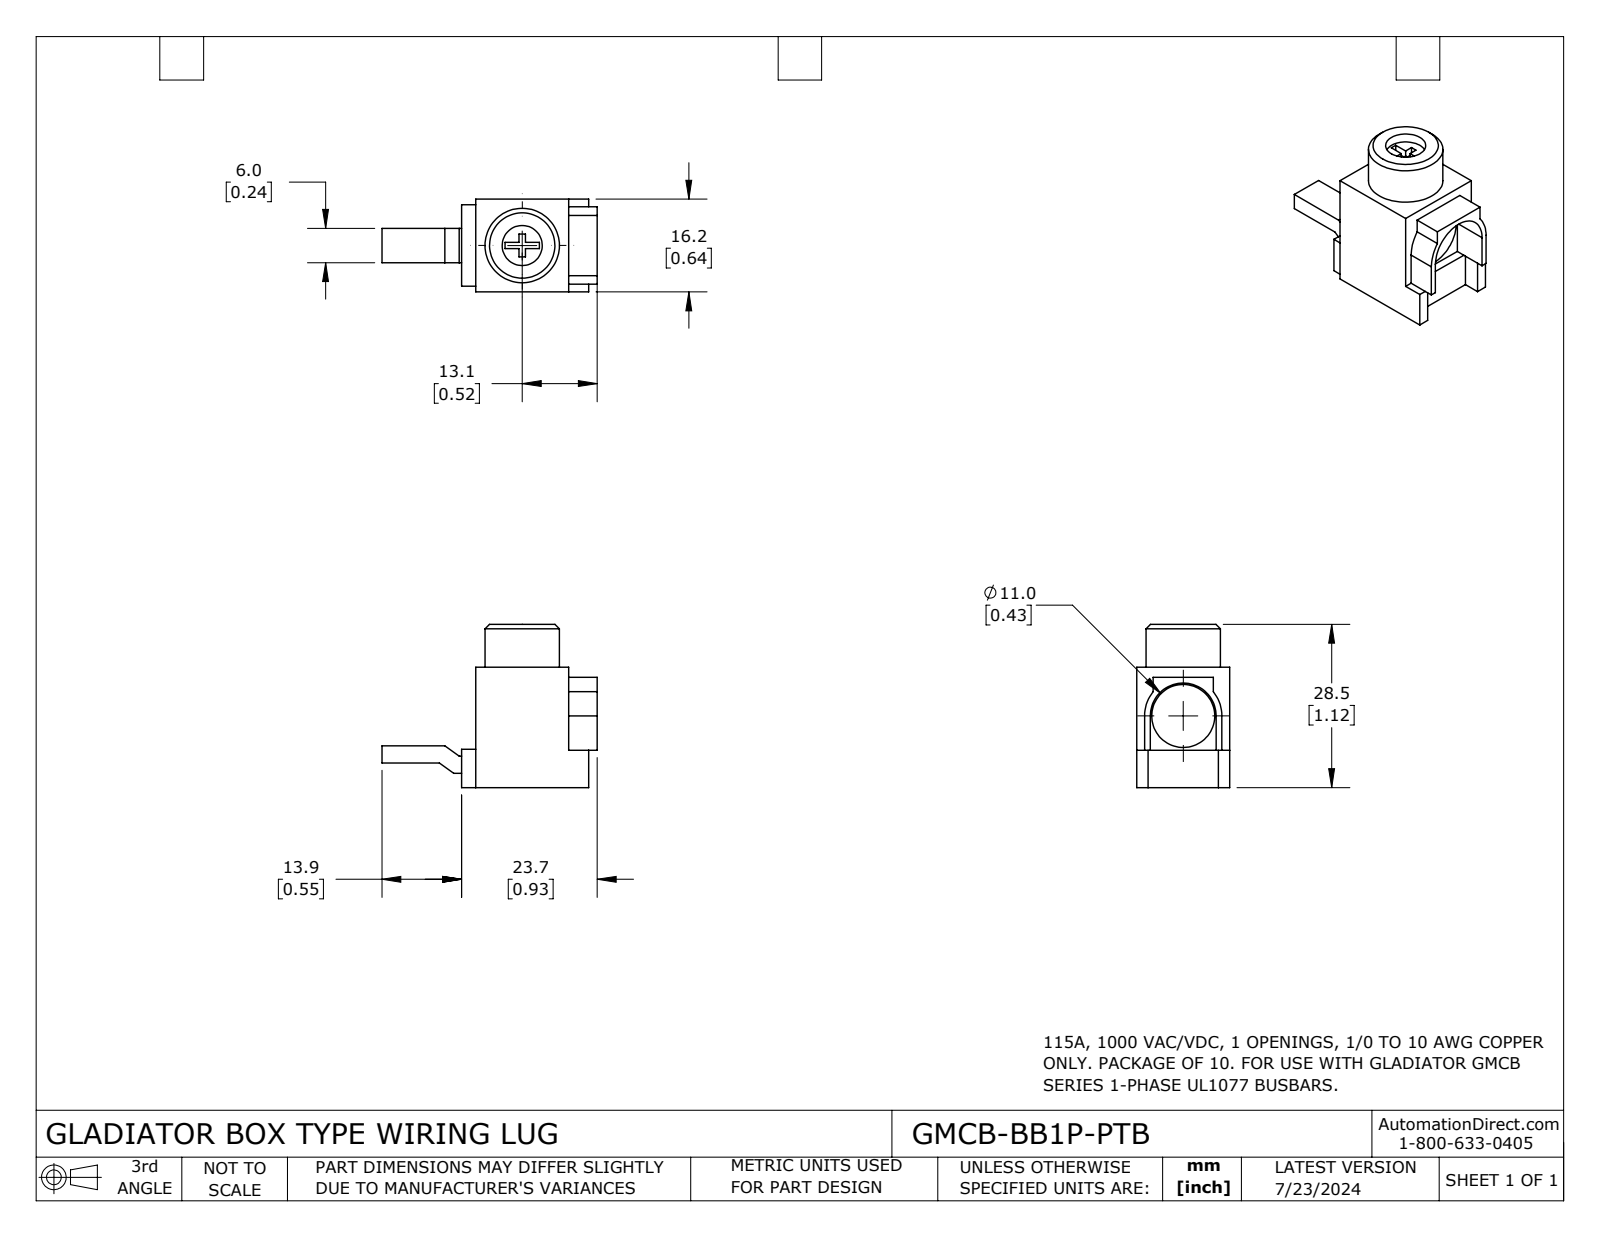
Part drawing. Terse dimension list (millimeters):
name: GMCB-BB1P-PTB
written by: SolidWorks 2023 (CONFIG_CONTROL_DESIGN)
unit: mm
bodies: 1 solid, 65 faces (54 planar, 9 cylindrical, 2 other)
size: 37.6 × 28.5 × 16.2
volume: 5 770 mm³; area: 3 593 mm²
holes: 1× ⌀7, 1× ⌀11
bosses: 1× ⌀13
rounds: 1× R5.7, 1× R6.8
face distances: 16.2, 16.7, 21, 1.1, 13.8, 3, 21.2, 15.1, 0.5, 1
